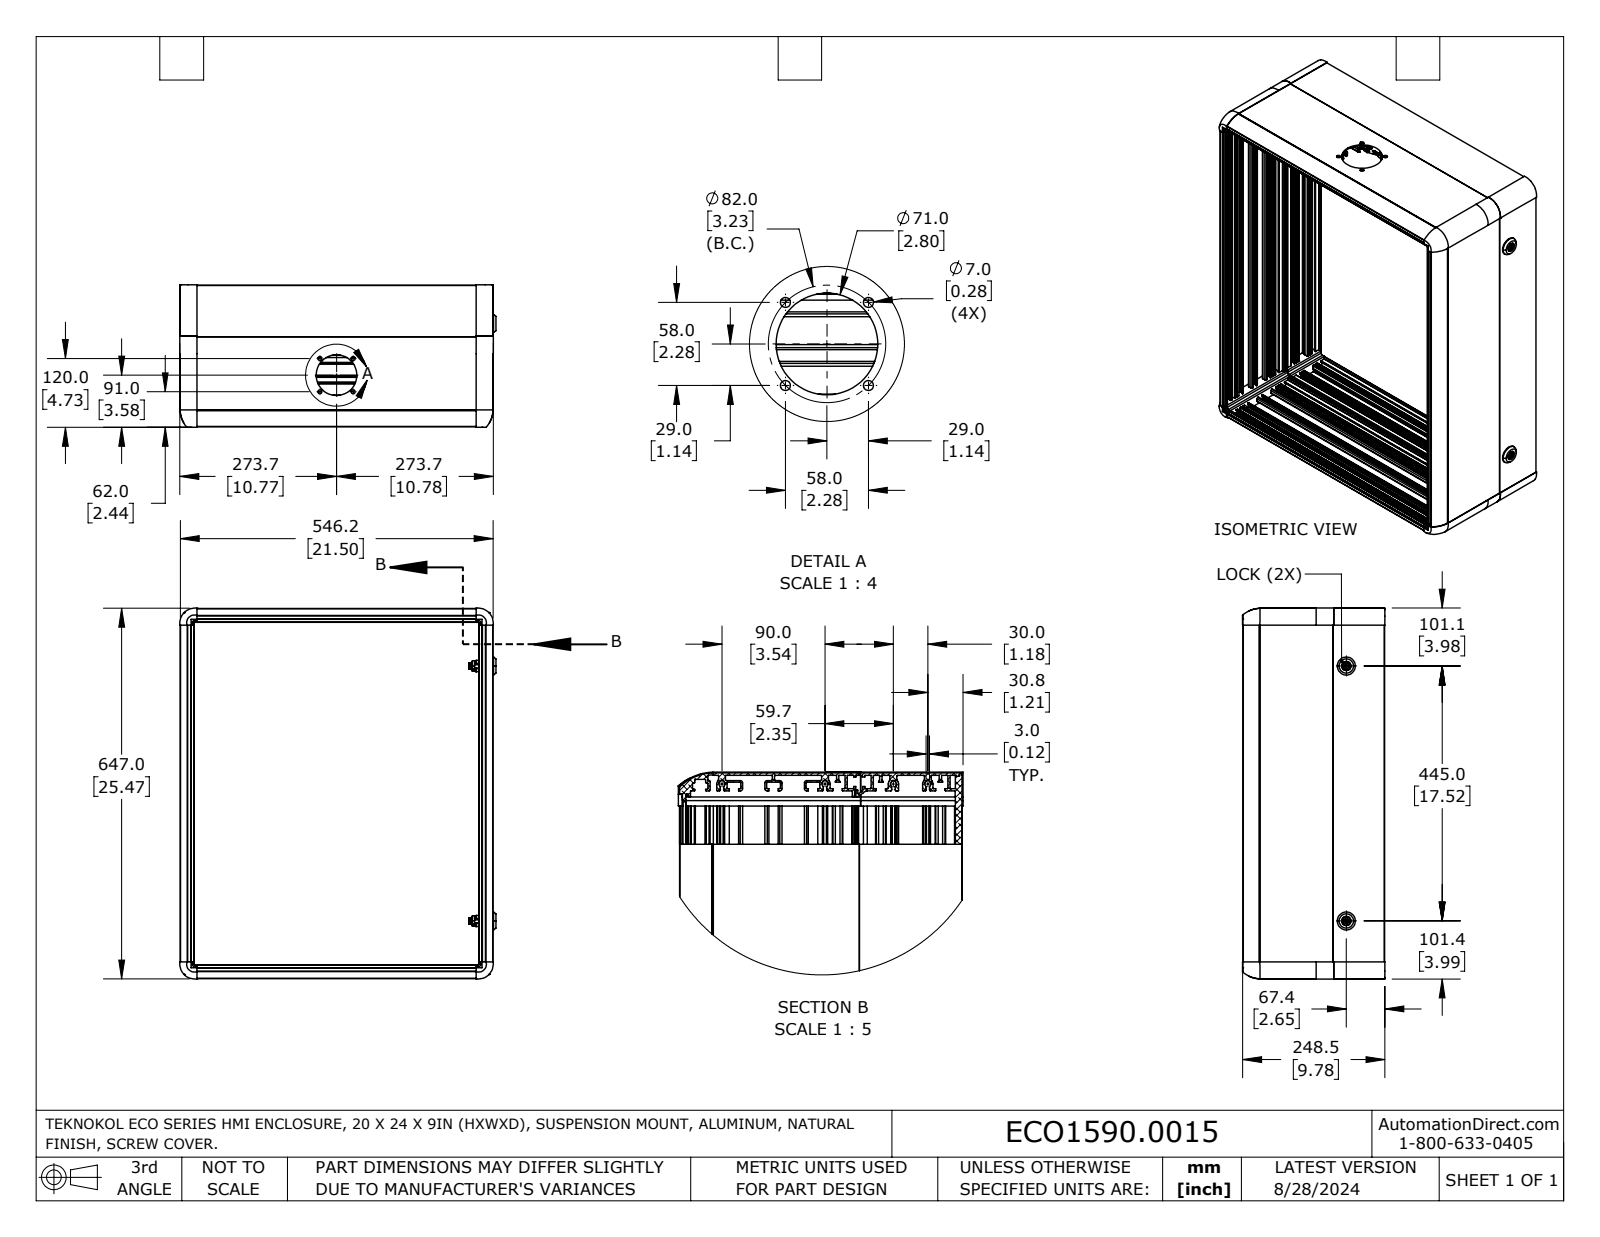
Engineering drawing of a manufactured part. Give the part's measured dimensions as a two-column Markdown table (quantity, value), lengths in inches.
| quantity | value |
| --- | --- |
| part name | ECO.1590.0015(500x600) |
| STEP written by | SolidWorks 2023 (AUTOMOTIVE_DESIGN) |
| units | inches |
| bodies | 24 solids, 2568 faces (1288 planar, 1014 cylindrical, 266 other) |
| overall size | 25.492 × 21.732 × 9.787 |
| volume | 346.6 in³ |
| surface area | 5 108 in² |
| round holes (diameter × count) | 0.205 × 4, 0.276 × 4, 0.197 × 2, 0.237 × 2, 0.394 × 2, 0.63 × 2, 2.795 × 1 |
| round bosses / shafts (diameter × count) | 0.374 × 4, 0.236 × 4, 1.24 × 2, 0.624 × 2, 0.531 × 2, 0.508 × 2, 0.382 × 2, 0.276 × 2 |
| partial cylindrical surfaces (radius × count) | 0.02 × 396, 0.039 × 84, 0.079 × 64, 0.008 × 48, 0.01 × 24, 0.016 × 20, 0.104 × 16, 0.128 × 16 |
| main face-to-face distances | 0.089, 0.233, 21.39, 25.327, 0.079, 21.478, 0.62, 0.531, 25.416, 21.301 |
| hole center spacings | 0.666, 1.615, 1.754, 2.283, 17.52, 1.181, 1.344, 3.229 |
